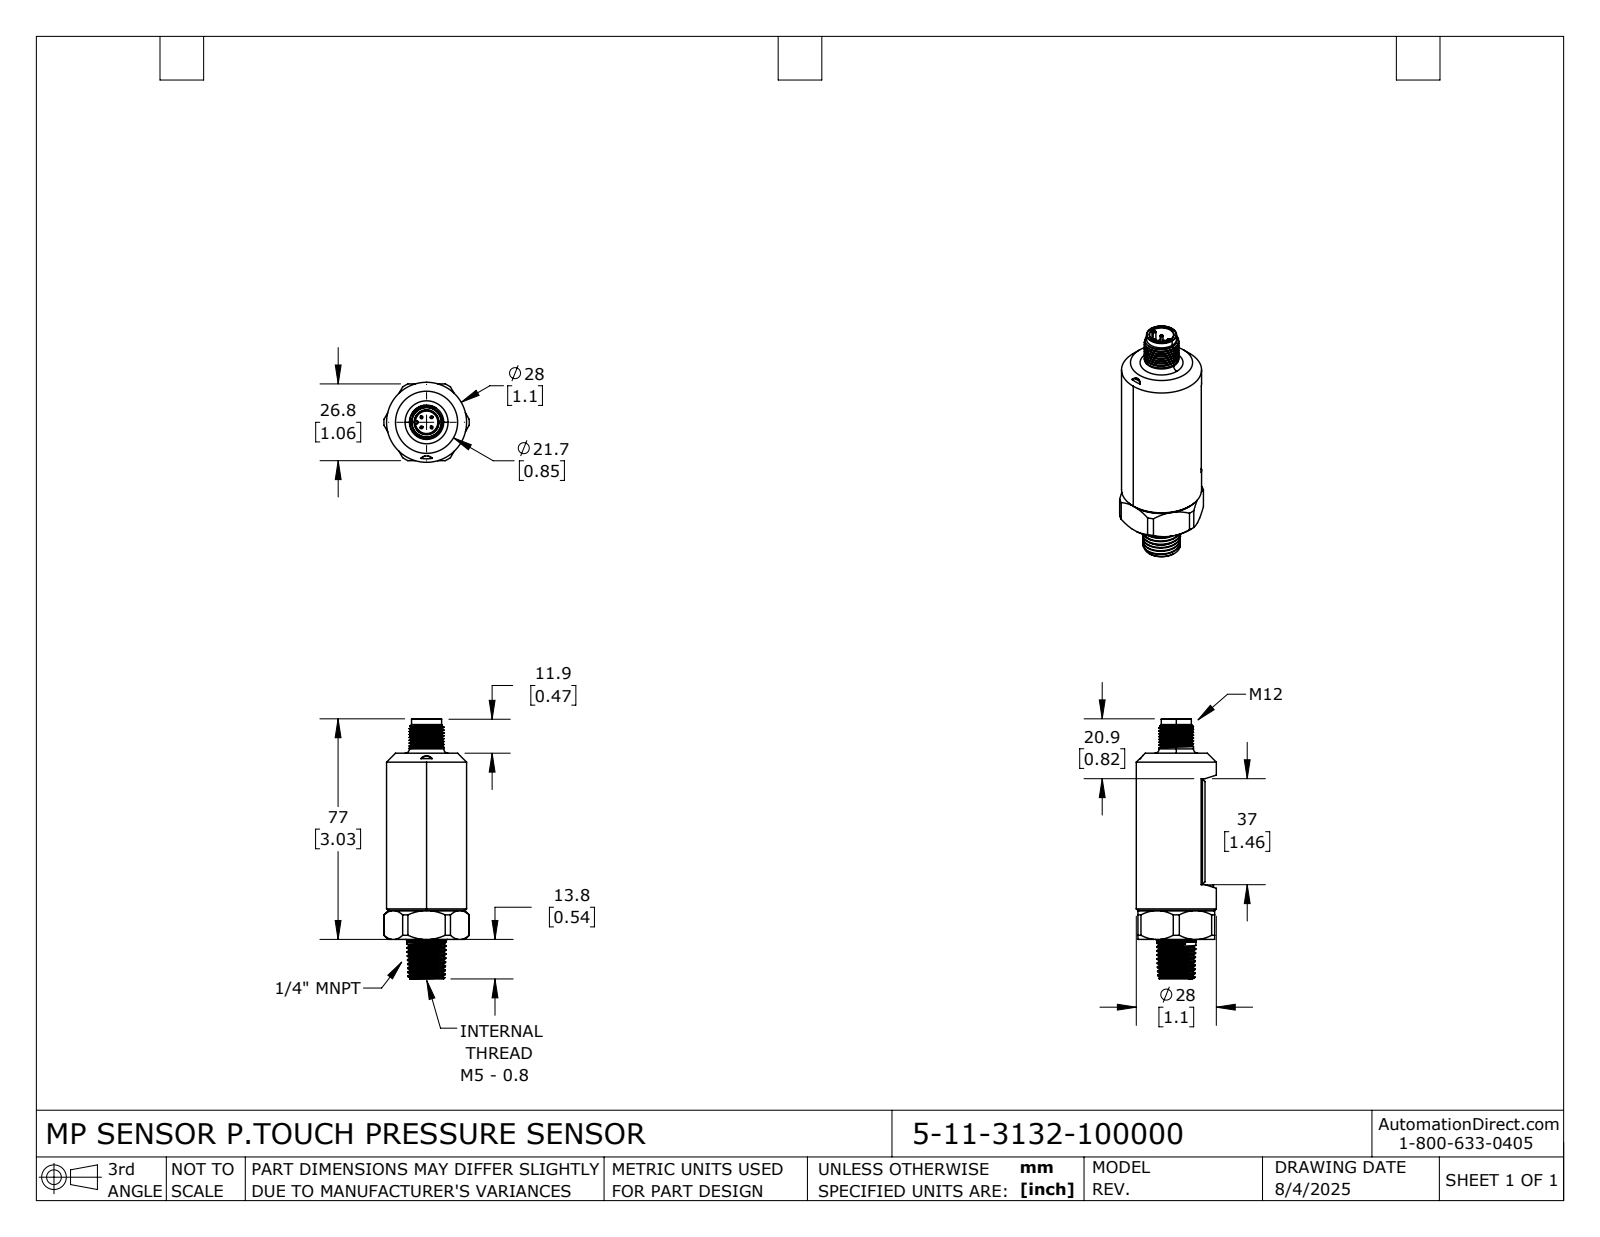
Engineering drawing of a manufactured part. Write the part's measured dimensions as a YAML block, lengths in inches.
part_name: "5-11-3132-100000"
step_written_by: "SolidWorks 2024 (AUTOMOTIVE_DESIGN)"
units: inches
bodies: {solids: 1, faces: 199, planar: 46, cylindrical: 68, other: 85}
overall_size: [3.575, 1.173, 1.1]
volume: 2.423
surface_area: 13.82
round_holes:
  - {diameter: 0.079, count: 1}
  - {diameter: 0.165, count: 1}
  - {diameter: 0.331, count: 1}
round_bosses_or_shafts:
  - {diameter: 0.039, count: 4}
  - {diameter: 1.1, count: 1}
  - {diameter: 1.024, count: 1}
  - {diameter: 0.539, count: 1}
  - {diameter: 0.472, count: 1}
  - {diameter: 0.413, count: 1}
partial_cylinders:
  - {radius: 0.006, count: 2}
  - {radius: 0.092, count: 1}
  - {radius: 0.587, count: 1}
face_to_face_distances: [1.055, 2.559, 0.922, 0.133, 0.543, 3.102, 0.354, 1.811, 0.35, 0.186]
